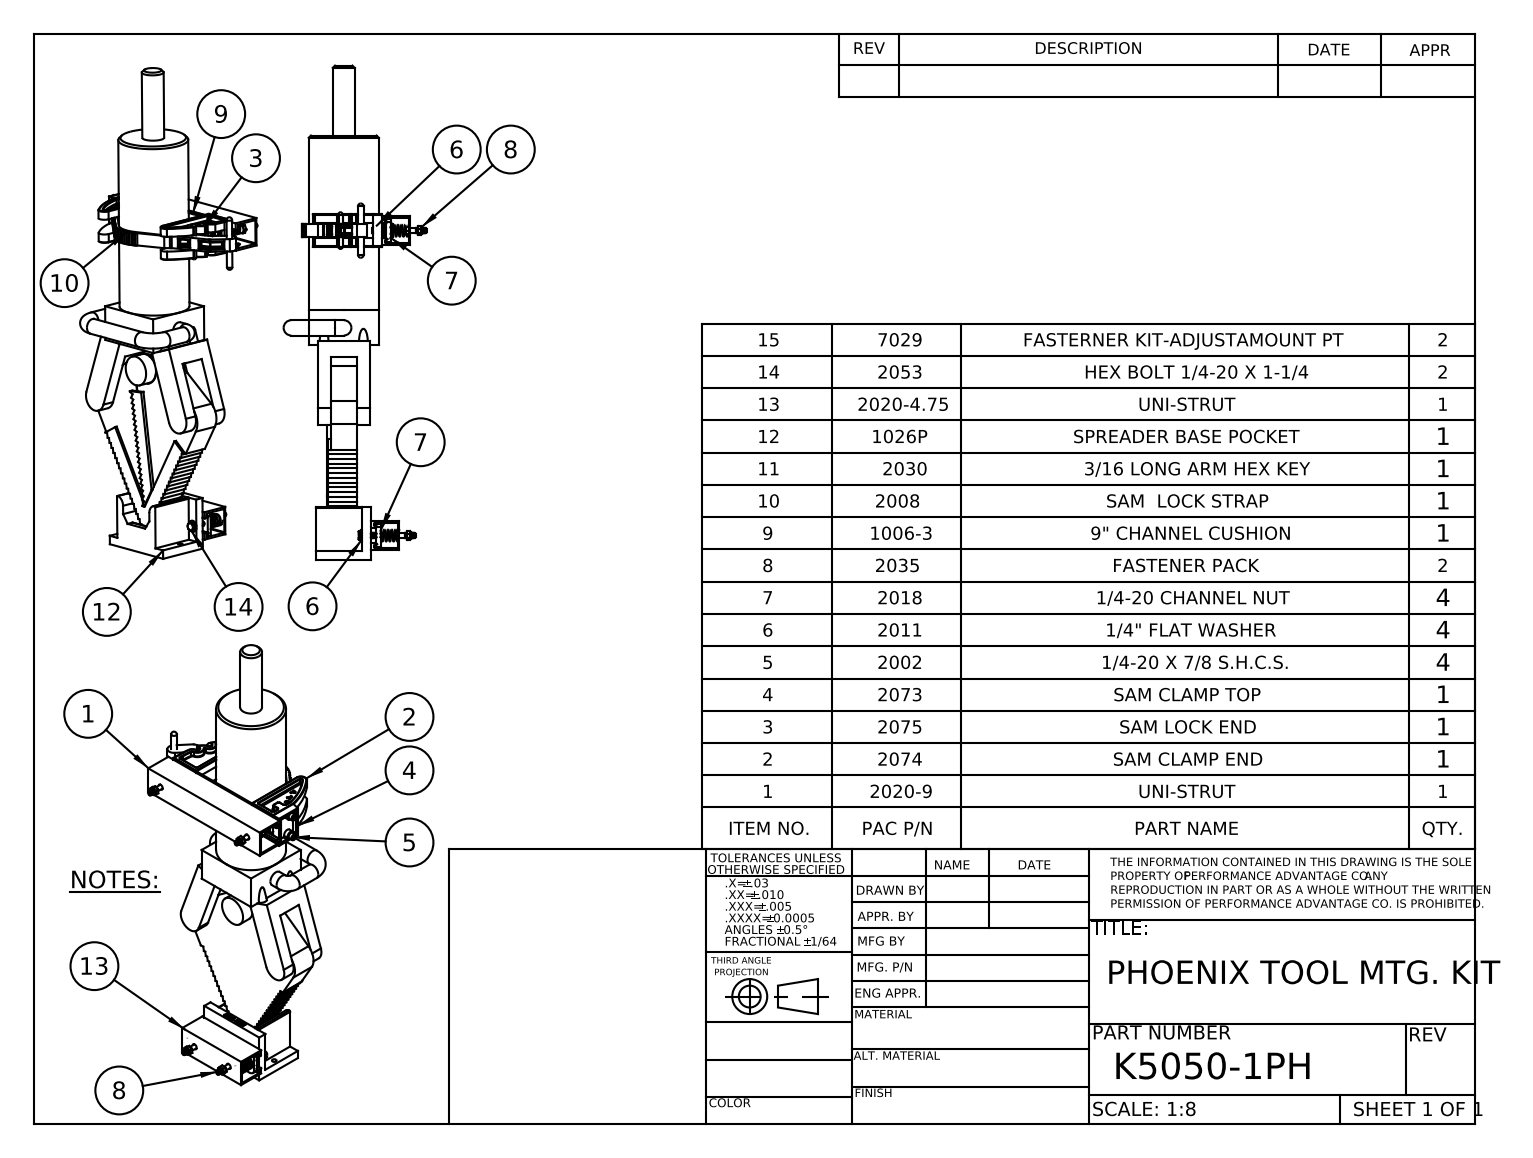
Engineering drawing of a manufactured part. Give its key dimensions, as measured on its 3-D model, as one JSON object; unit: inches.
{"part_name": "2053_HFBOLT 0.25-20x1.25x0.75-C; K5050-1PH; 2035_7\" apart; 2075 (+8 more)", "step_written_by": "SolidWorks 2014 (CONFIG_CONTROL_DESIGN)", "units": "inches", "bodies": {"solids": 33, "faces": 2058, "planar": 723, "cylindrical": 605, "other": 730}, "overall_size": [28.25, 10.365, 8.173], "volume_in3": 326.6, "surface_area_in2": 912.1, "round_holes": [[0.201, 10], [0.266, 6], [0.269, 4], [0.288, 4], [0.332, 4], [0.25, 3], [1.76, 1]], "round_bosses_or_shafts": [[0.25, 9], [0.875, 4], [0.625, 4], [0.5, 4], [0.404, 4], [0.375, 4], [0.438, 2], [4, 1]], "partial_cylinders_radius": [[0.062, 56], [0.031, 46], [0.063, 19], [0.062, 12], [0.03, 8], [0.06, 8], [0.125, 8], [0.424, 8]], "face_to_face_distances": [1.625, 1.25, 2.25, 3.063, 0.5, 1.5, 0.625, 0.109, 1.516, 0.75], "hole_center_spacings": [9.426, 17.567, 18.106, 0.563, 3.312, 3.875, 8.835, 9.524]}
